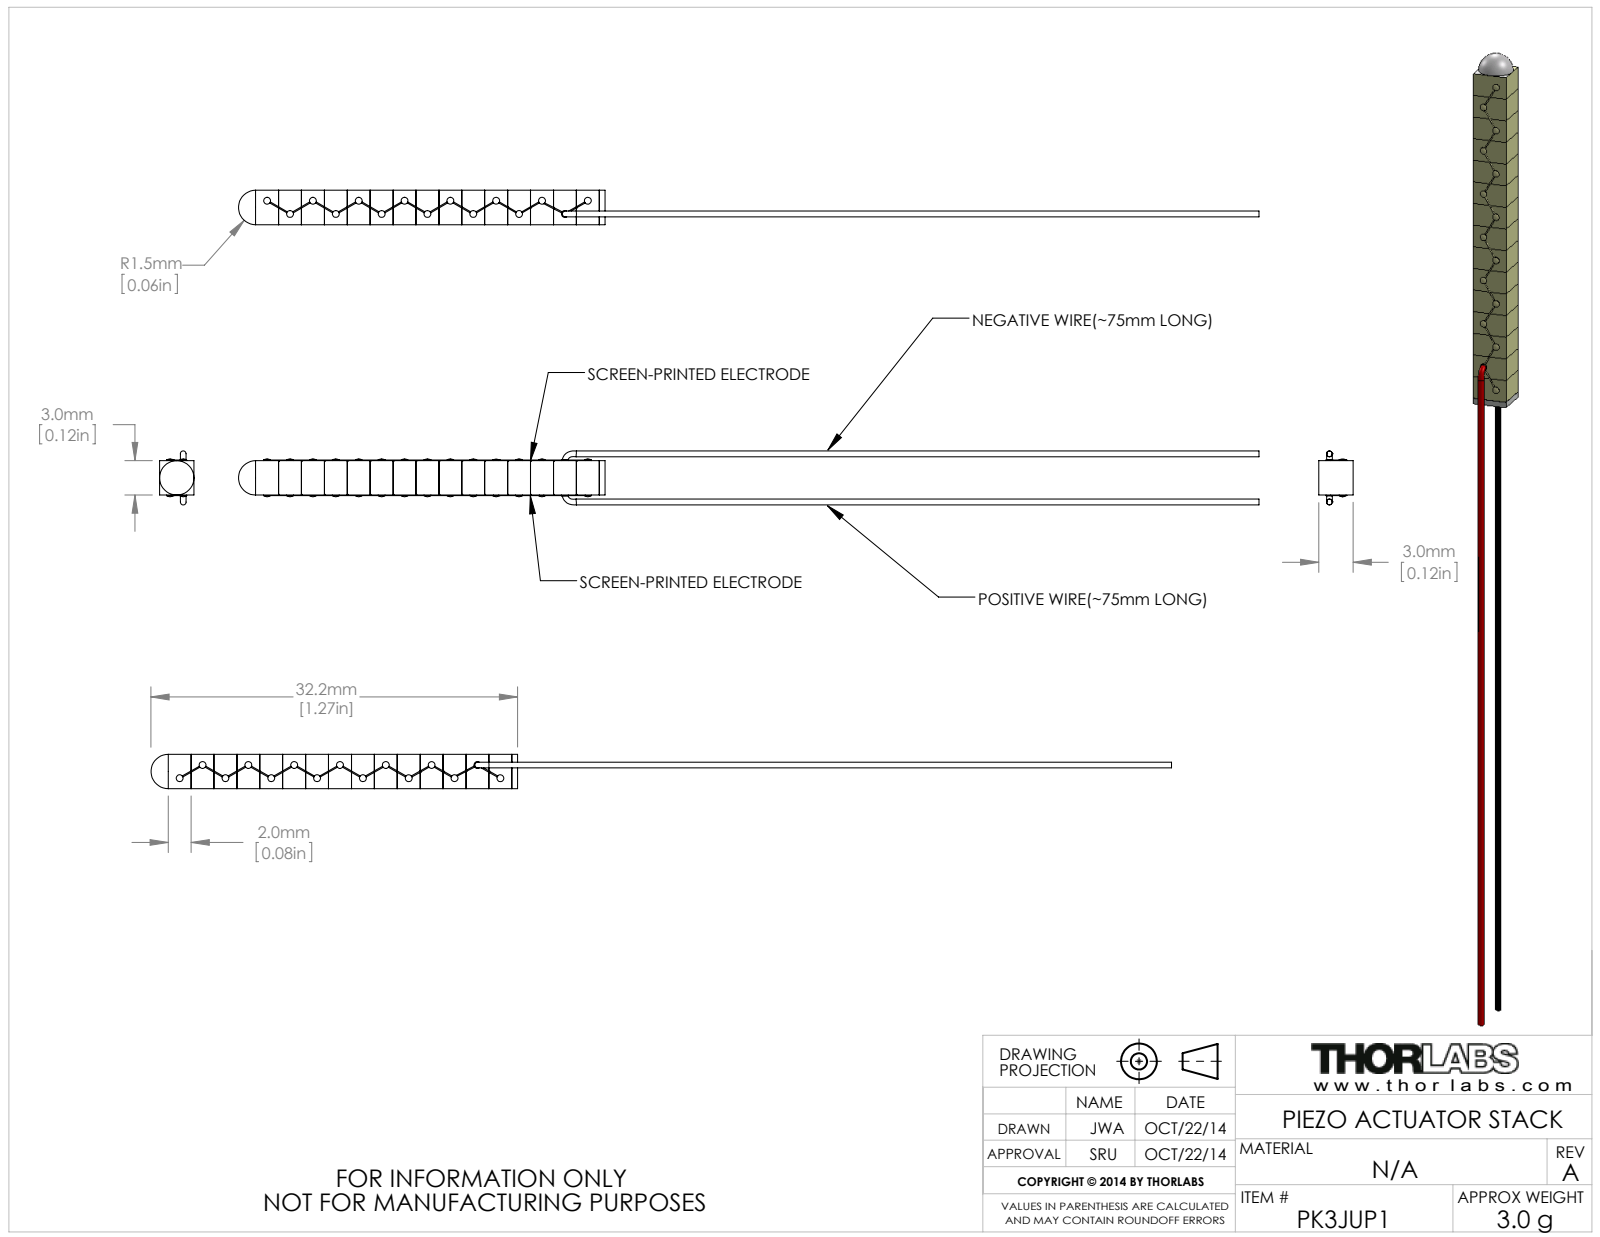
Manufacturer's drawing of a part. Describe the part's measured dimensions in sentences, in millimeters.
The part is named "PK3JUP1". Its 3-D file was written by "SolidWorks 2012 (AUTOMOTIVE_DESIGN)". It is 19 solids with 312 faces: 118 planar, 126 cylindrical and 68 other. Overall it measures 89.1 by 4.72 by 3 millimeters. Its volume is 307 cubic millimeters and its surface area 876 square millimeters. Round bosses or shafts: 15 of diameter 0.6. The main face-to-face distances are 2, 4, 6, 8, 3, 10, 12, 14, 16, 18.
